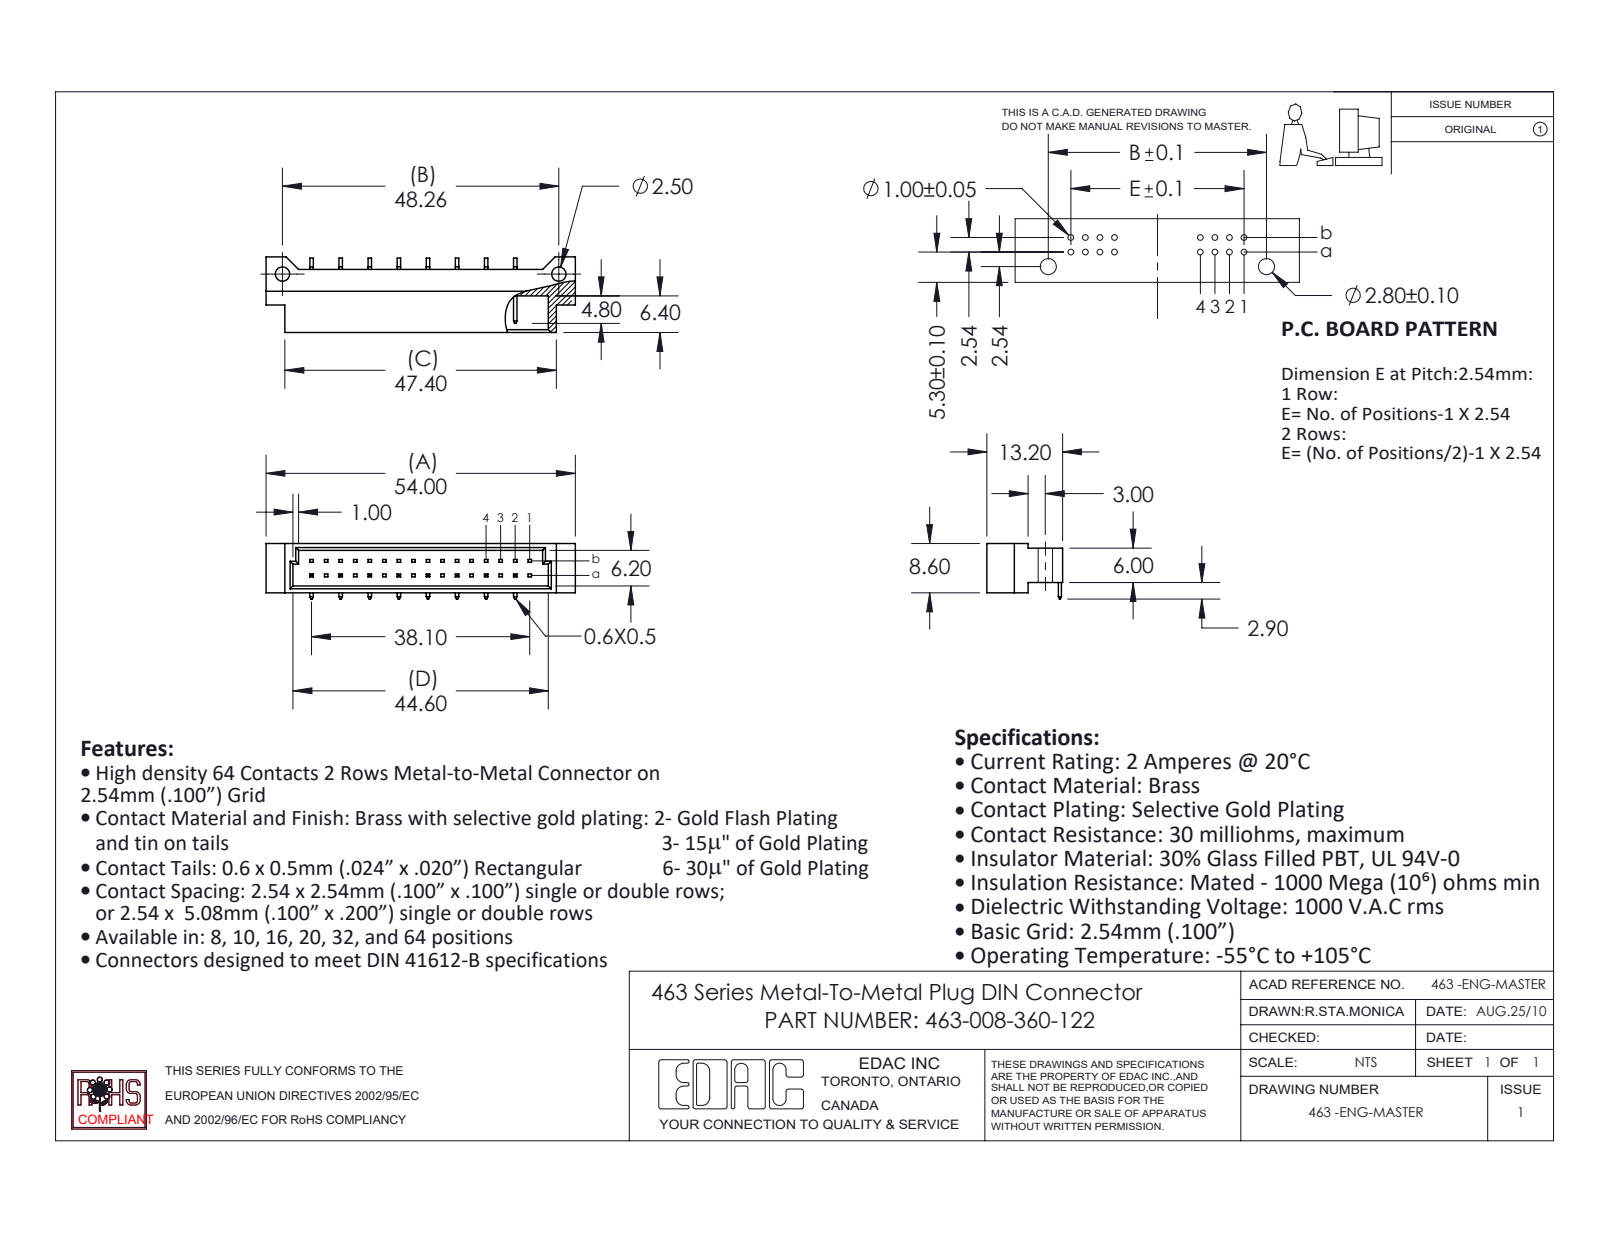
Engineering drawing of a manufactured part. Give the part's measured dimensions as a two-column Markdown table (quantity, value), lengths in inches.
| quantity | value |
| --- | --- |
| part name | 463 Part_32; 463-290-1; 463-008-360-122 |
| STEP written by | SolidWorks 2020 (CONFIG_CONTROL_DESIGN) |
| units | inches |
| bodies | 9 solids, 311 faces (291 planar, 20 cylindrical, 0 other) |
| overall size | 2.126 × 0.52 × 0.382 |
| volume | 0.159 in³ |
| surface area | 5.513 in² |
| round holes (diameter × count) | 0.098 × 2 |
| partial cylindrical surfaces (radius × count) | 0.04 × 1, 0.06 × 1 |
| main face-to-face distances | 0.047, 0.291, 0.339, 0.031, 0.244, 0.024, 0.236, 0.268, 0.181, 0.22 |
| hole center spacings | 1.9 |
